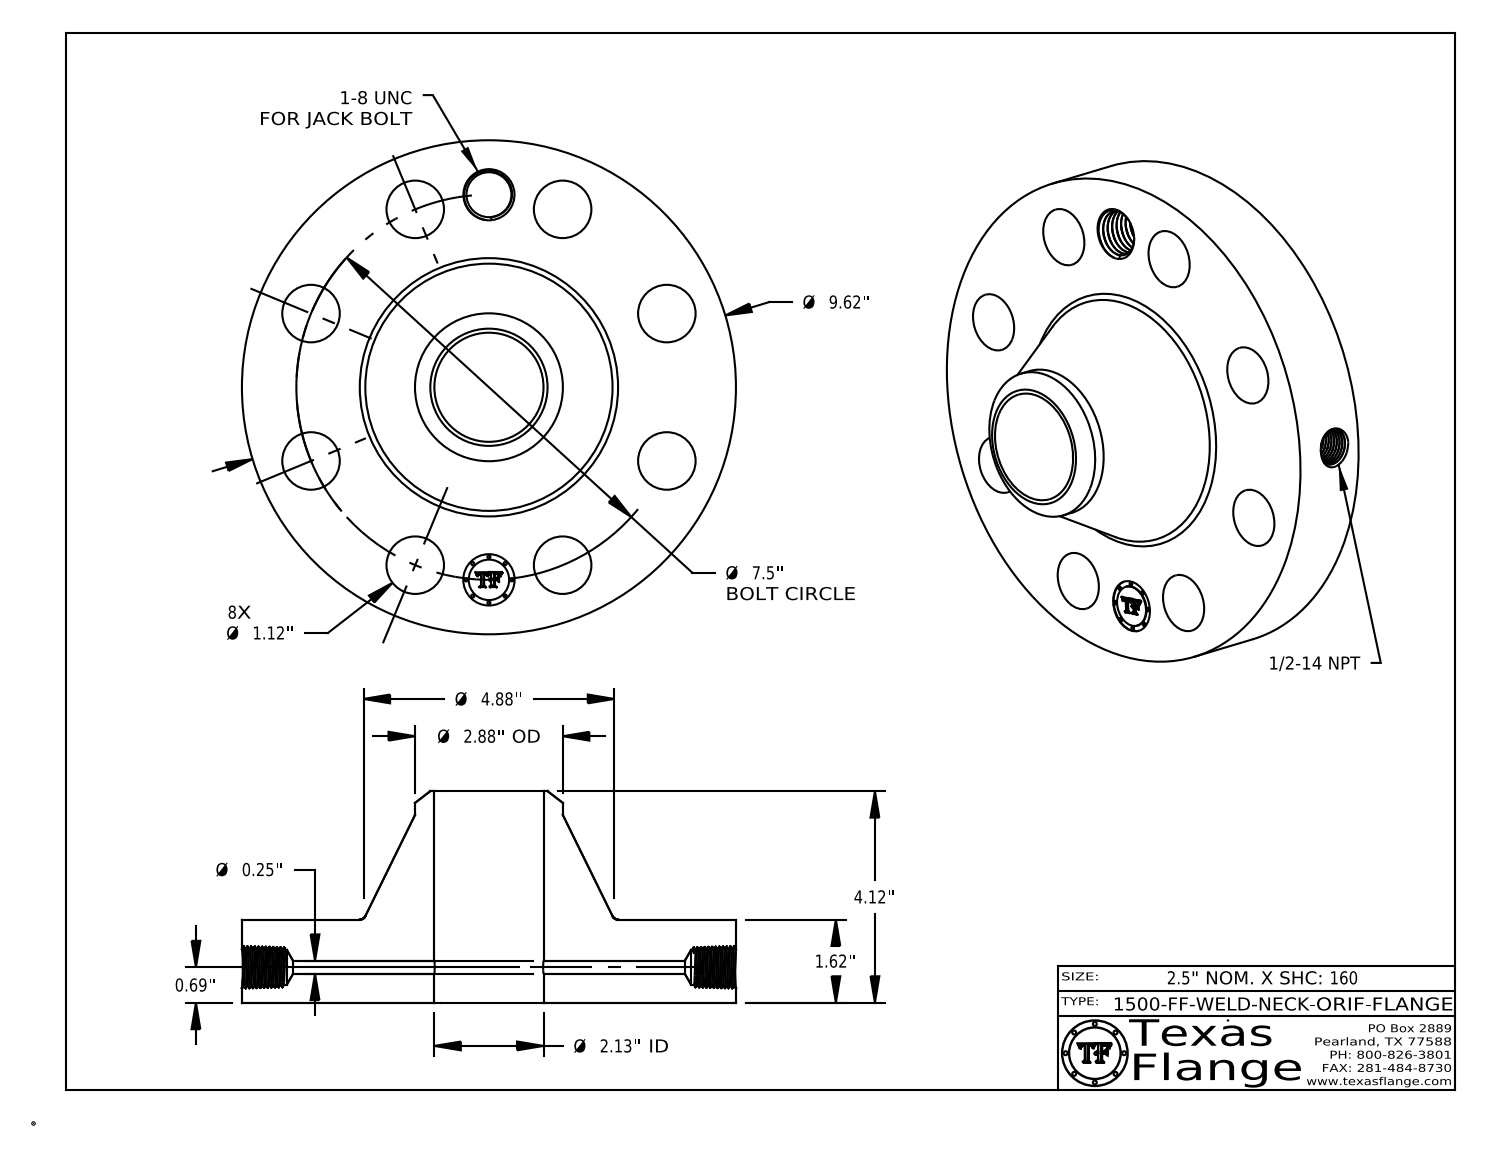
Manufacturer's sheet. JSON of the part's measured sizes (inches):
{"part_name": "1500-FF-WELD-NECK", "step_written_by": "CATIA V5 STEP AP214 (AUTOMOTIVE_DESIGN)", "units": "inches", "bodies": {"solids": 1, "faces": 756, "planar": 368, "cylindrical": 87, "other": 301}, "overall_size": [9.62, 9.62, 4.12], "volume_in3": 115.5, "surface_area_in2": 279.2, "round_holes": [[1.12, 8], [0.25, 1], [0.672, 1], [0.875, 1], [1, 1], [2.125, 1]], "round_bosses_or_shafts": [[0.061, 8], [9.62, 1], [2.88, 1], [0.788, 1]], "face_to_face_distances": [1.62, 4.12, 2.5, 1.605, 0.015, 2.515, 0.298, 0.293, 0.054, 0.248], "hole_center_spacings": [3.75, 2.87, 5.303, 6.929, 7.5, 1.463, 4.167, 6.236]}
